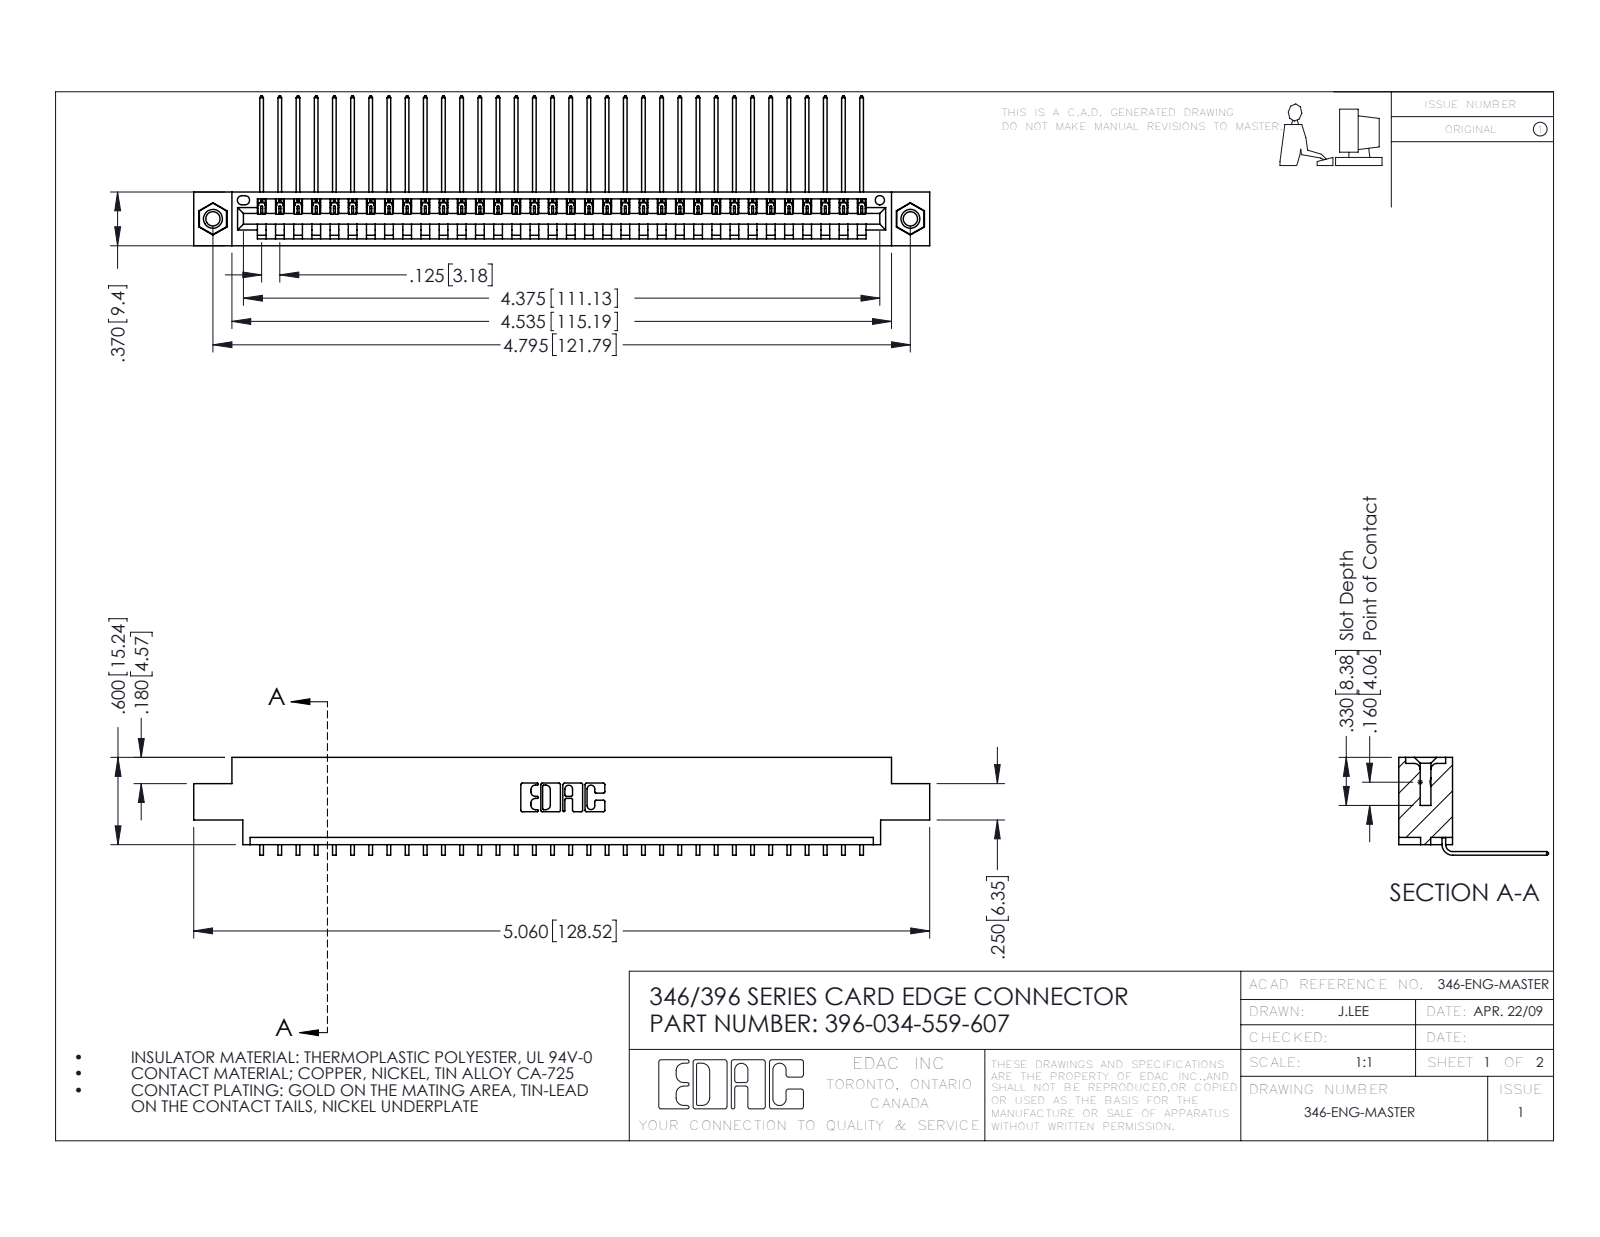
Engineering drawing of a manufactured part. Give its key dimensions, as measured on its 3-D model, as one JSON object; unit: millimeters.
{"part_name": "345-250-001_345-250-005-103; 346 Part_0.170 Offset - 0.156 Dia-TI; 345-292-001_558 559 Tail - 1; 396-034-559-607", "step_written_by": "SolidWorks 2016 (CONFIG_CONTROL_DESIGN)", "units": "millimeters", "bodies": {"solids": 37, "faces": 2226, "planar": 1540, "cylindrical": 670, "other": 16}, "overall_size": [128.5, 26.2, 17.1], "volume_mm3": 12200, "surface_area_mm2": 16030, "round_holes": [[2.5, 2], [3.2, 2], [4, 2], [1.6, 1]], "round_bosses_or_shafts": [[3.9, 2]], "partial_cylinders_radius": [[0.2, 68], [0.3, 22], [0.2, 6], [0.8, 6], [0.7, 3], [0.8, 2], [1, 2], [0.4, 1]], "face_to_face_distances": [1.2, 8.2, 9.4, 0.6, 6.4, 1.8, 5.6, 3.8, 7.6, 2.5], "hole_center_spacings": [6.2, 116.5, 121.8]}
